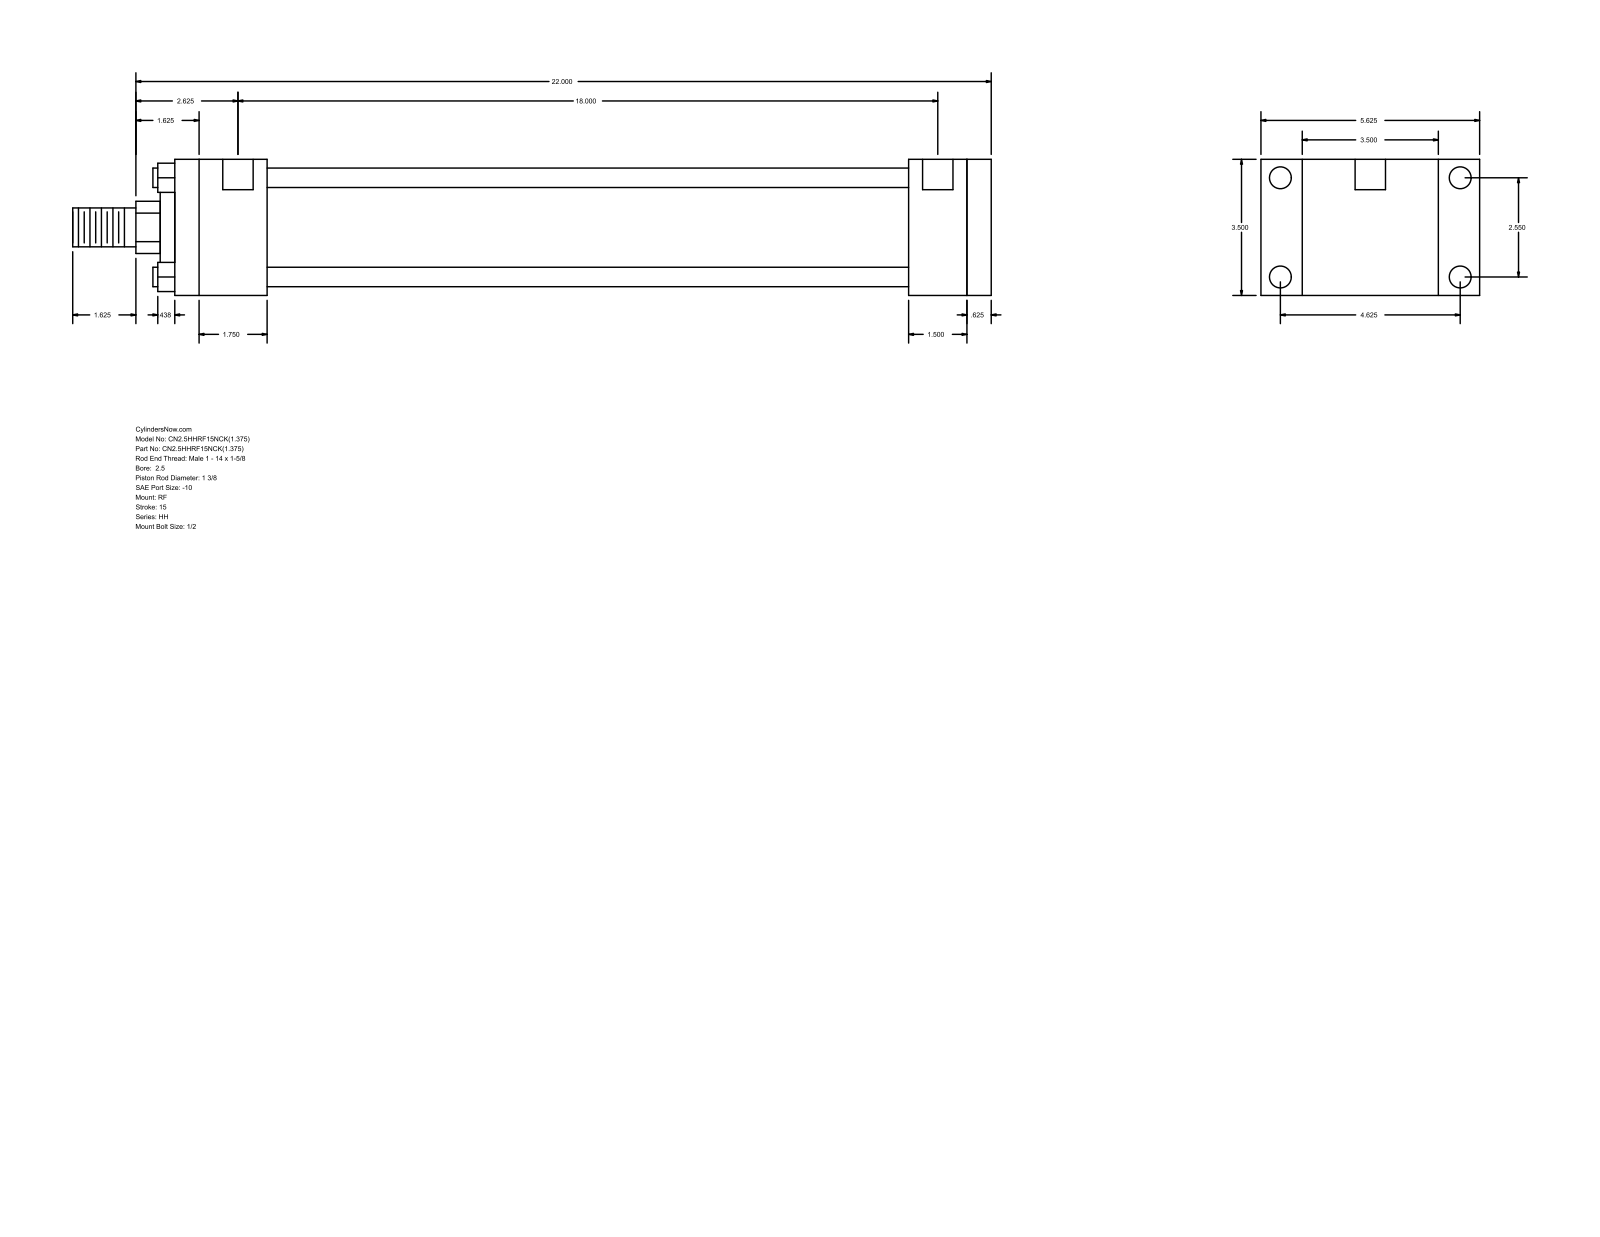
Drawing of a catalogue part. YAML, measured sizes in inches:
part_name: "HH_RF__0250_1.375"
step_written_by: "GSSL Pune (CONFIG_CONTROL_DESIGN)"
units: inches
bodies: {solids: 0, faces: 92, planar: 64, cylindrical: 28, other: 0}
overall_size: [23.625, 5.625, 3.5]
round_holes:
  - {diameter: 0.219, count: 4}
  - {diameter: 0.563, count: 4}
  - {diameter: 0.781, count: 2}
round_bosses_or_shafts:
  - {diameter: 0.5, count: 4}
  - {diameter: 2.875, count: 1}
  - {diameter: 2, count: 1}
  - {diameter: 1.375, count: 1}
  - {diameter: 1, count: 1}
partial_cylinders:
  - {radius: 0.672, count: 1}
face_to_face_distances: [3.5, 21, 0.625, 20.375, 2.375, 18, 18.625, 18.875, 16.5, 1.5]
hole_center_spacings: [0.062, 2.55, 4.625, 5.281, 18.063, 18.125, 18]
